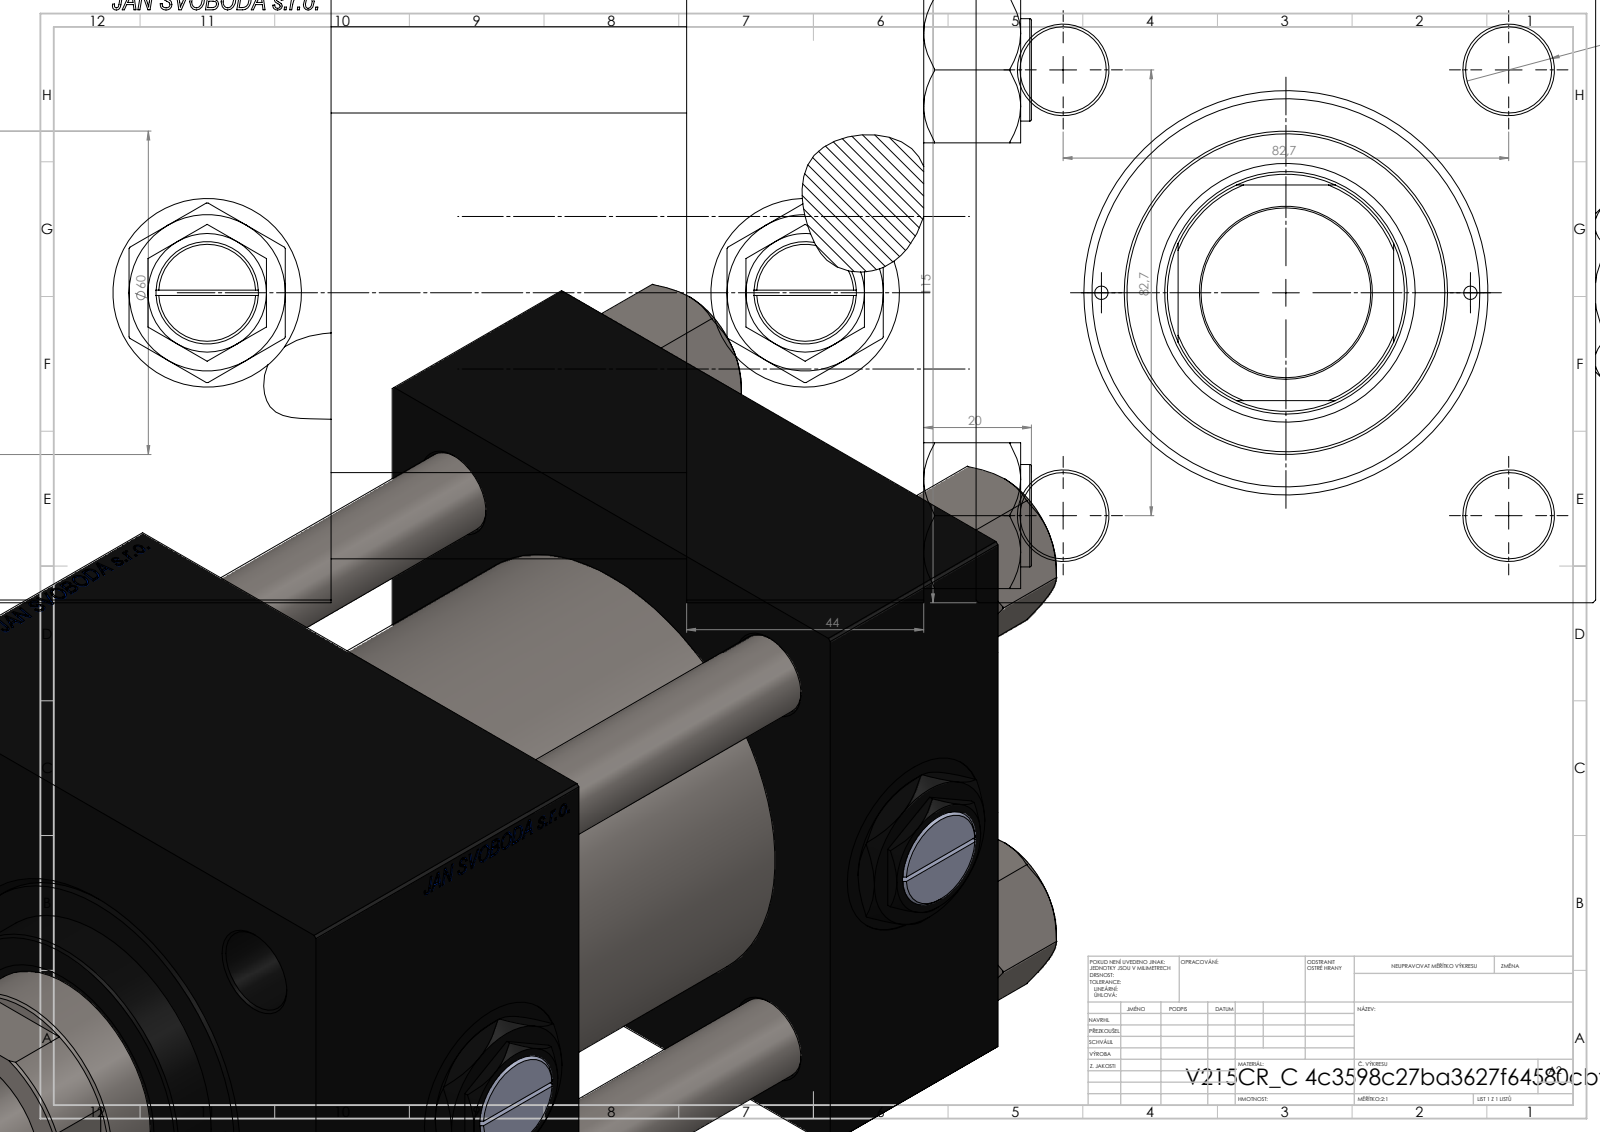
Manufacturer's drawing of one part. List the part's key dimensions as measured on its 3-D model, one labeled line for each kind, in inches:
Part name (STEP PRODUCT): V215CR_C_Body; V215CR_C_TYCINKA; V215_VC_A; Zatka_pro_OIL_PORT (+2 more)
STEP written by: SolidWorks 2019 (CONFIG_CONTROL_DESIGN)
Units: inches
Bodies: 13 solids, 1303 faces (623 planar, 102 cylindrical, 578 other)
Overall size (bounding box): 9.055 × 4.803 × 4.528
Volume: 110.1 in³ · Surface area: 435.4 in²
Round holes (diameter × count): ⌀0.63 ×4, ⌀0.098 ×2, ⌀0.276 ×2, ⌀1.041 ×2, ⌀1.378 ×2, ⌀1.24 ×1, ⌀1.772 ×1, ⌀1.89 ×1, ⌀2.402 ×1, ⌀2.835 ×1, ⌀3.15 ×1
Round bosses / shafts (diameter × count): ⌀0.748 ×4, ⌀3.386 ×1, ⌀2.362 ×1
Partial cylindrical surfaces — rounded edges, fillets, slot ends (radius × count): R0.866 ×1
Main face-to-face distances: 4.528, 1.732, 4.331, 7.047, 5.315, 2.717, 2.598, 0.787, 5.917, 4.185
Hole centre spacings: 1.652, 2.302, 3.256, 3.393, 1.348, 4.605, 2.697, 4.37
